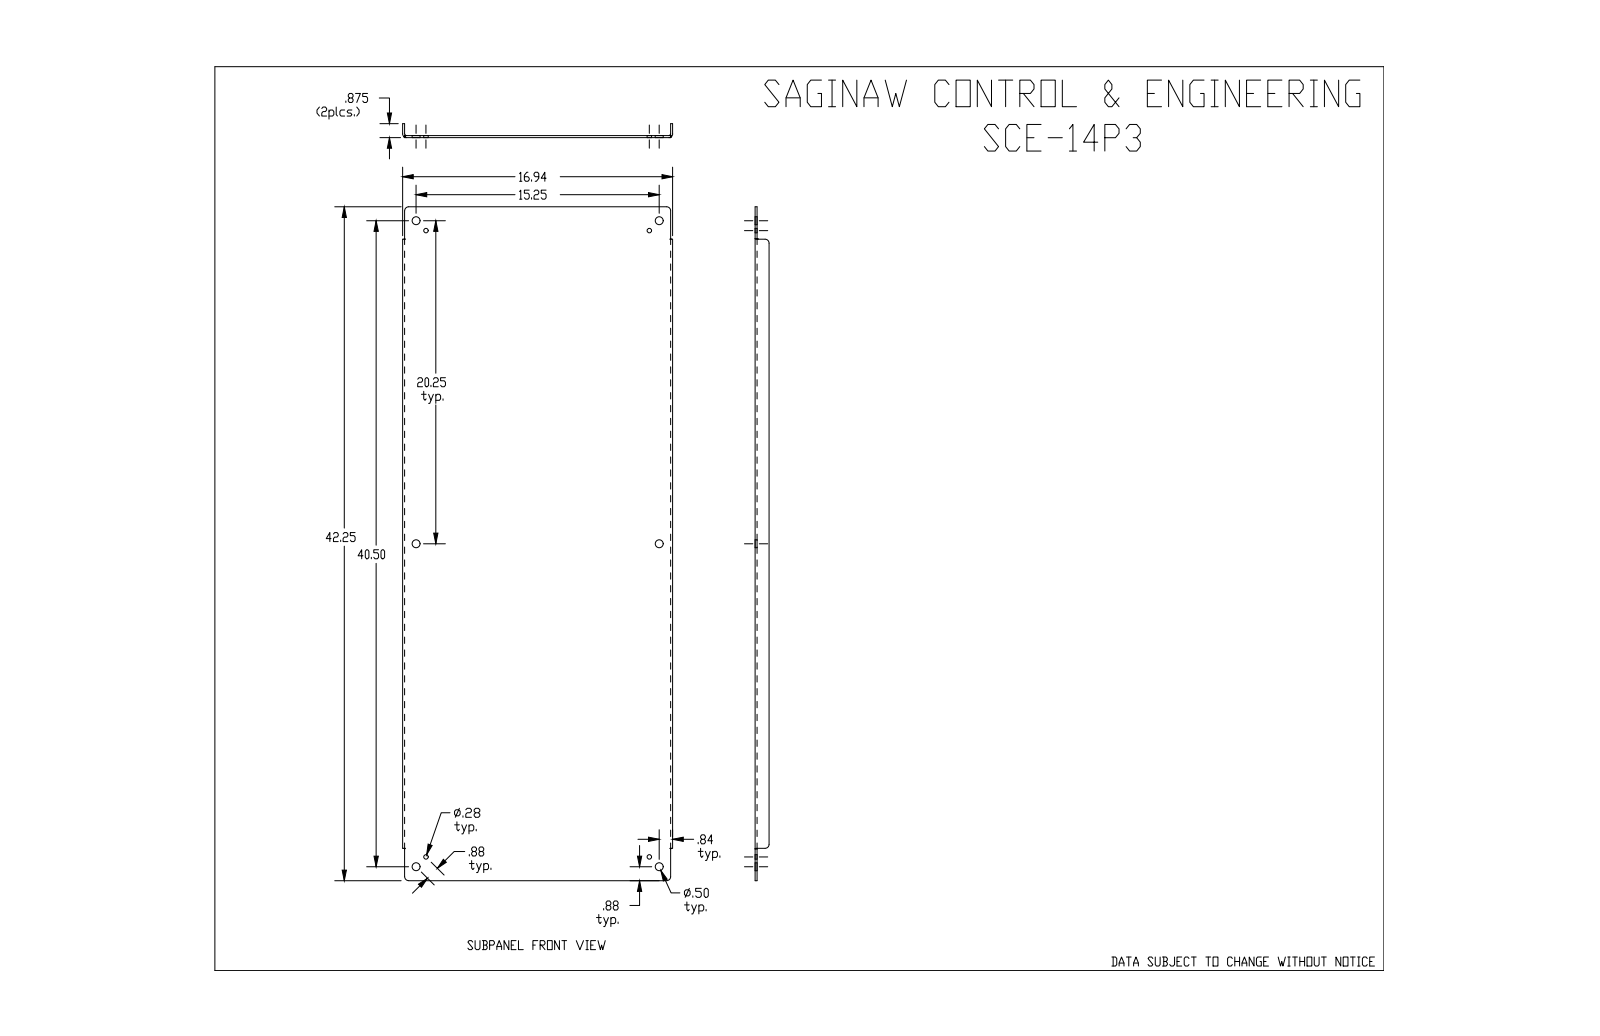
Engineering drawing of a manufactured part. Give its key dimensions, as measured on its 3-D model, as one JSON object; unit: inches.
{"part_name": "SCE-14P3", "step_written_by": "SolidWorks 2019 (CONFIG_CONTROL_DESIGN)", "units": "inches", "bodies": {"solids": 1, "faces": 52, "planar": 18, "cylindrical": 22, "other": 12}, "overall_size": [42.25, 16.938, 0.875], "volume_in3": 95.58, "surface_area_in2": 1546, "round_holes": [[0.5, 6], [0.281, 4]], "partial_cylinders_radius": [[0.25, 6], [0.112, 2], [0.237, 2]], "face_to_face_distances": [0.125, 0.125, 16.813, 16.687, 16.938, 0.75, 0.875, 42.25, 2.031, 40.219], "hole_center_spacings": [0.875, 14.644, 19.641, 20.25, 24.483, 25.35, 39.886, 42.48]}
